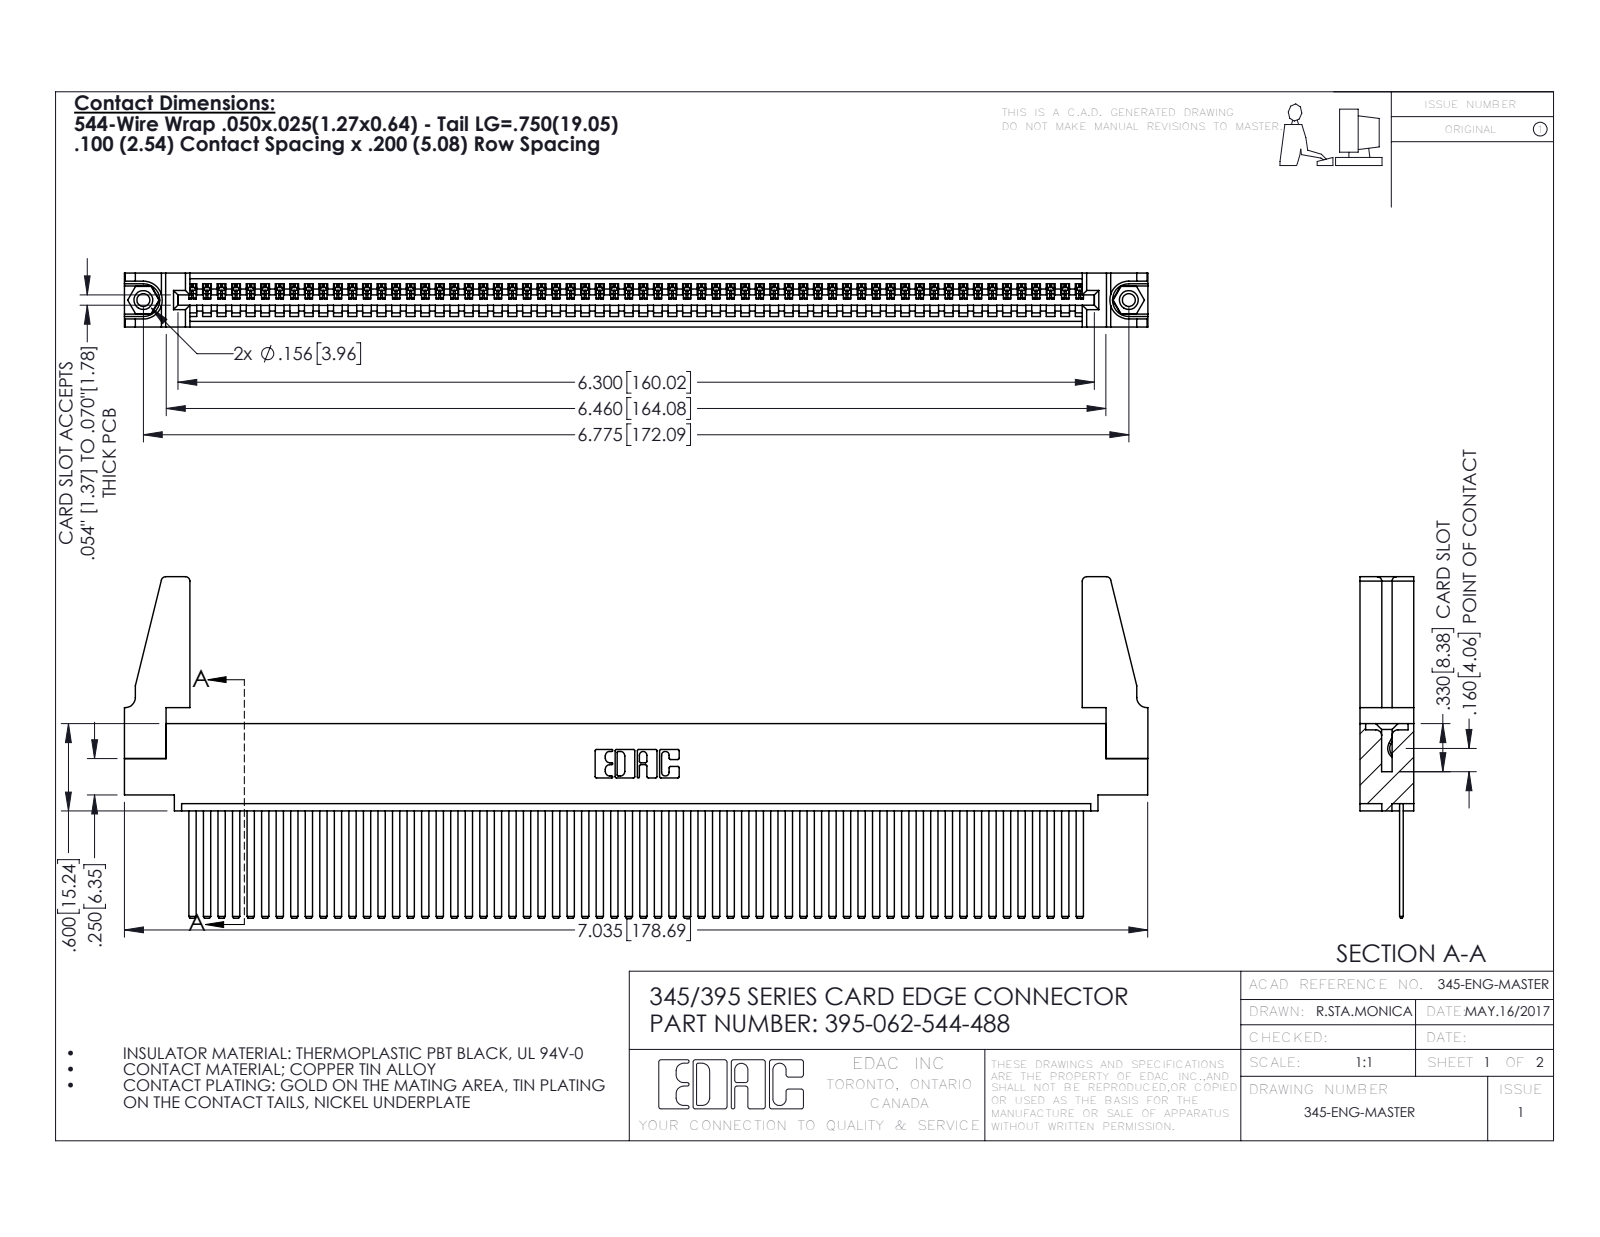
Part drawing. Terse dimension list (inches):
name: 345 Part_0.110 Offset - 0.156 Dia-TH; 345-220-078_345-220-088; 395-062-544-488; 345-250-001_345-250-001-102 (+1 more)
written by: SolidWorks 2016 (CONFIG_CONTROL_DESIGN)
unit: in
bodies: 67 solids, 3478 faces (2388 planar, 1074 cylindrical, 16 other)
size: 7.036 × 2.347 × 0.37
volume: 1.284 in³; area: 45.37 in²
holes: 2× ⌀0.089, 2× ⌀0.125, 2× ⌀0.156, 1× ⌀0.064
bosses: 2× ⌀0.155
rounds: 124× R0.006, 22× R0.01, 8× R0.03, 6× R0.007, 6× R0.031, 3× R0.026, 2× R0.031, 2× R0.04
face distances: 0.072, 0.298, 0.098, 0.272, 0.025, 0.37, 0.2, 0.225, 0.149, 0.072
hole spacings: 0.27, 6.539, 6.775
